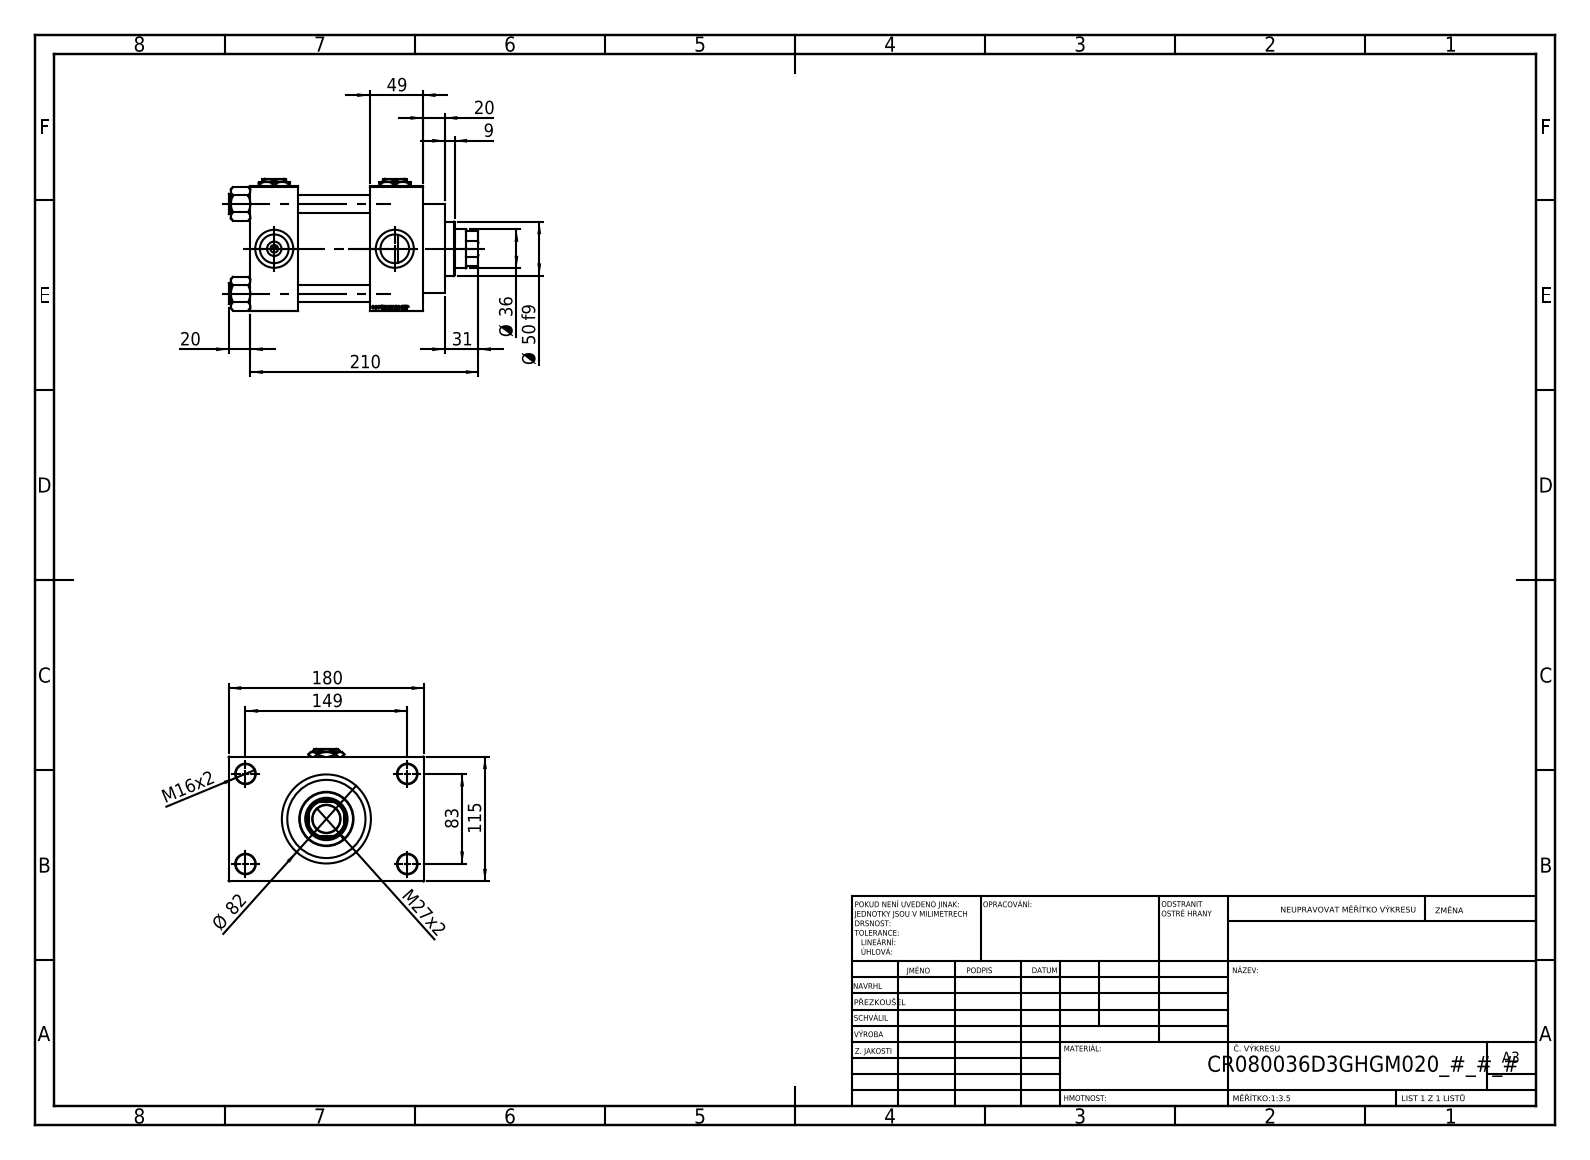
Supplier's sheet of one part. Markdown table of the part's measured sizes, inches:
| quantity | value |
| --- | --- |
| part name | V215CR_D_Body; V215_VC_A; Zatka_pro_OIL_PORT; V215CR_VCP_D (+2 more) |
| STEP written by | SolidWorks 2019 (CONFIG_CONTROL_DESIGN) |
| units | inches |
| bodies | 13 solids, 1252 faces (593 planar, 99 cylindrical, 560 other) |
| overall size | 9.055 × 7.087 × 4.803 |
| volume | 120 in³ |
| surface area | 470.1 in² |
| round holes (diameter × count) | 0.63 × 4, 0.709 × 4, 1.041 × 4, 1.378 × 4, 0.276 × 3, 1.004 × 1, 1.417 × 1, 1.535 × 1, 2.402 × 1, 2.835 × 1, 3.15 × 1 |
| round bosses / shafts (diameter × count) | 0.748 × 4, 3.386 × 1, 3.228 × 1, 1.969 × 1 |
| partial cylindrical surfaces (radius × count) | 0.689 × 1 |
| main face-to-face distances | 4.528, 2.598, 4.331, 1.929, 1.732, 6.26, 1.28, 5.807, 0.787, 2.717 |
| hole center spacings | 1.305, 2.302, 3.256, 3.357, 3.513, 4.561, 5.607, 3.268 |
